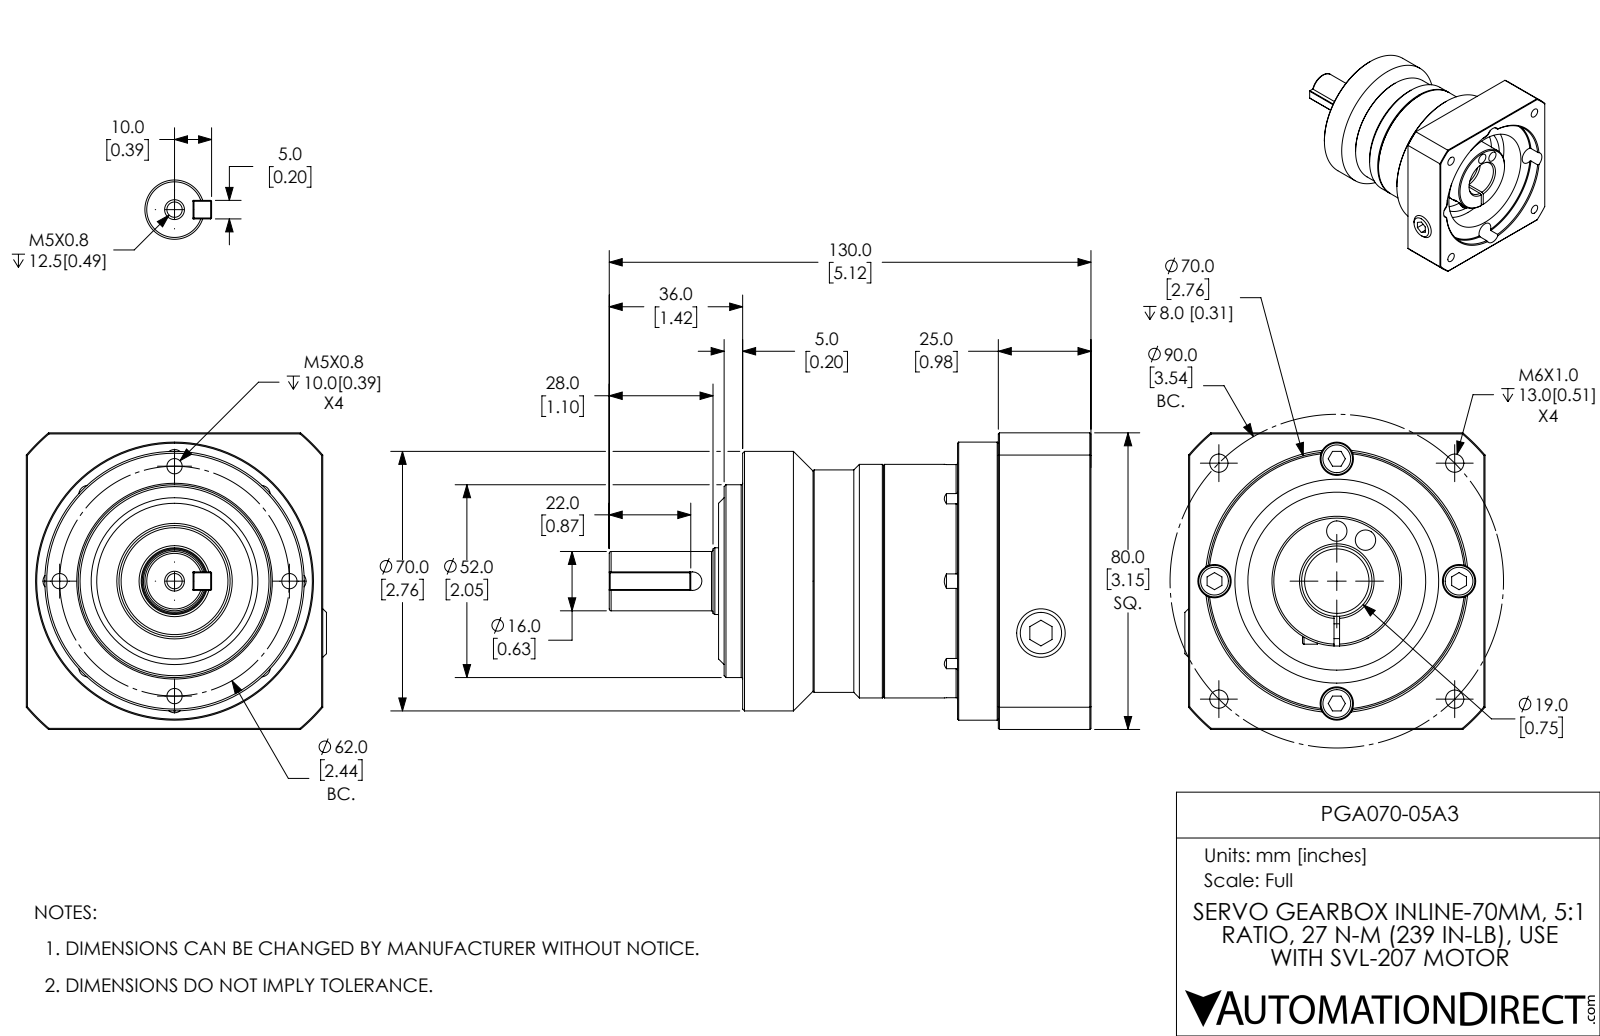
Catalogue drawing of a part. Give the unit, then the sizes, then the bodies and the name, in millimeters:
Units: millimetres
Overall size (bounding box): 130 × 81 × 80
Round holes (diameter × count): ⌀5 ×8, ⌀4.1 ×5, ⌀4.9 ×4, ⌀9 ×4, ⌀5.5 ×2, ⌀3.3 ×1, ⌀4.5 ×1, ⌀10.5 ×1, ⌀19 ×1, ⌀48 ×1, ⌀55 ×1, ⌀70 ×1
Round bosses / shafts (diameter × count): ⌀8.5 ×4, ⌀75 ×1, ⌀63 ×1, ⌀60 ×1, ⌀52 ×1, ⌀35 ×1, ⌀18 ×1, ⌀16 ×1
Partial cylindrical surfaces — rounded edges, fillets, slot ends (radius × count): R2.5 ×1, R4 ×1, R52.5 ×1
Main face-to-face distances: 80, 25, 6, 19, 94, 11, 69, 17, 36, 88
Hole centre spacings: 24.6, 25.2, 31.8, 31.9, 45.3, 55.8, 59.1, 61
Volume: 345 600 mm³ · Surface area: 53 840 mm²
Bodies: 1 solid, 360 faces (123 planar, 100 cylindrical, 137 other)
Part name (STEP PRODUCT): PGA070-05A3
STEP written by: SolidWorks 2019 (CONFIG_CONTROL_DESIGN)
